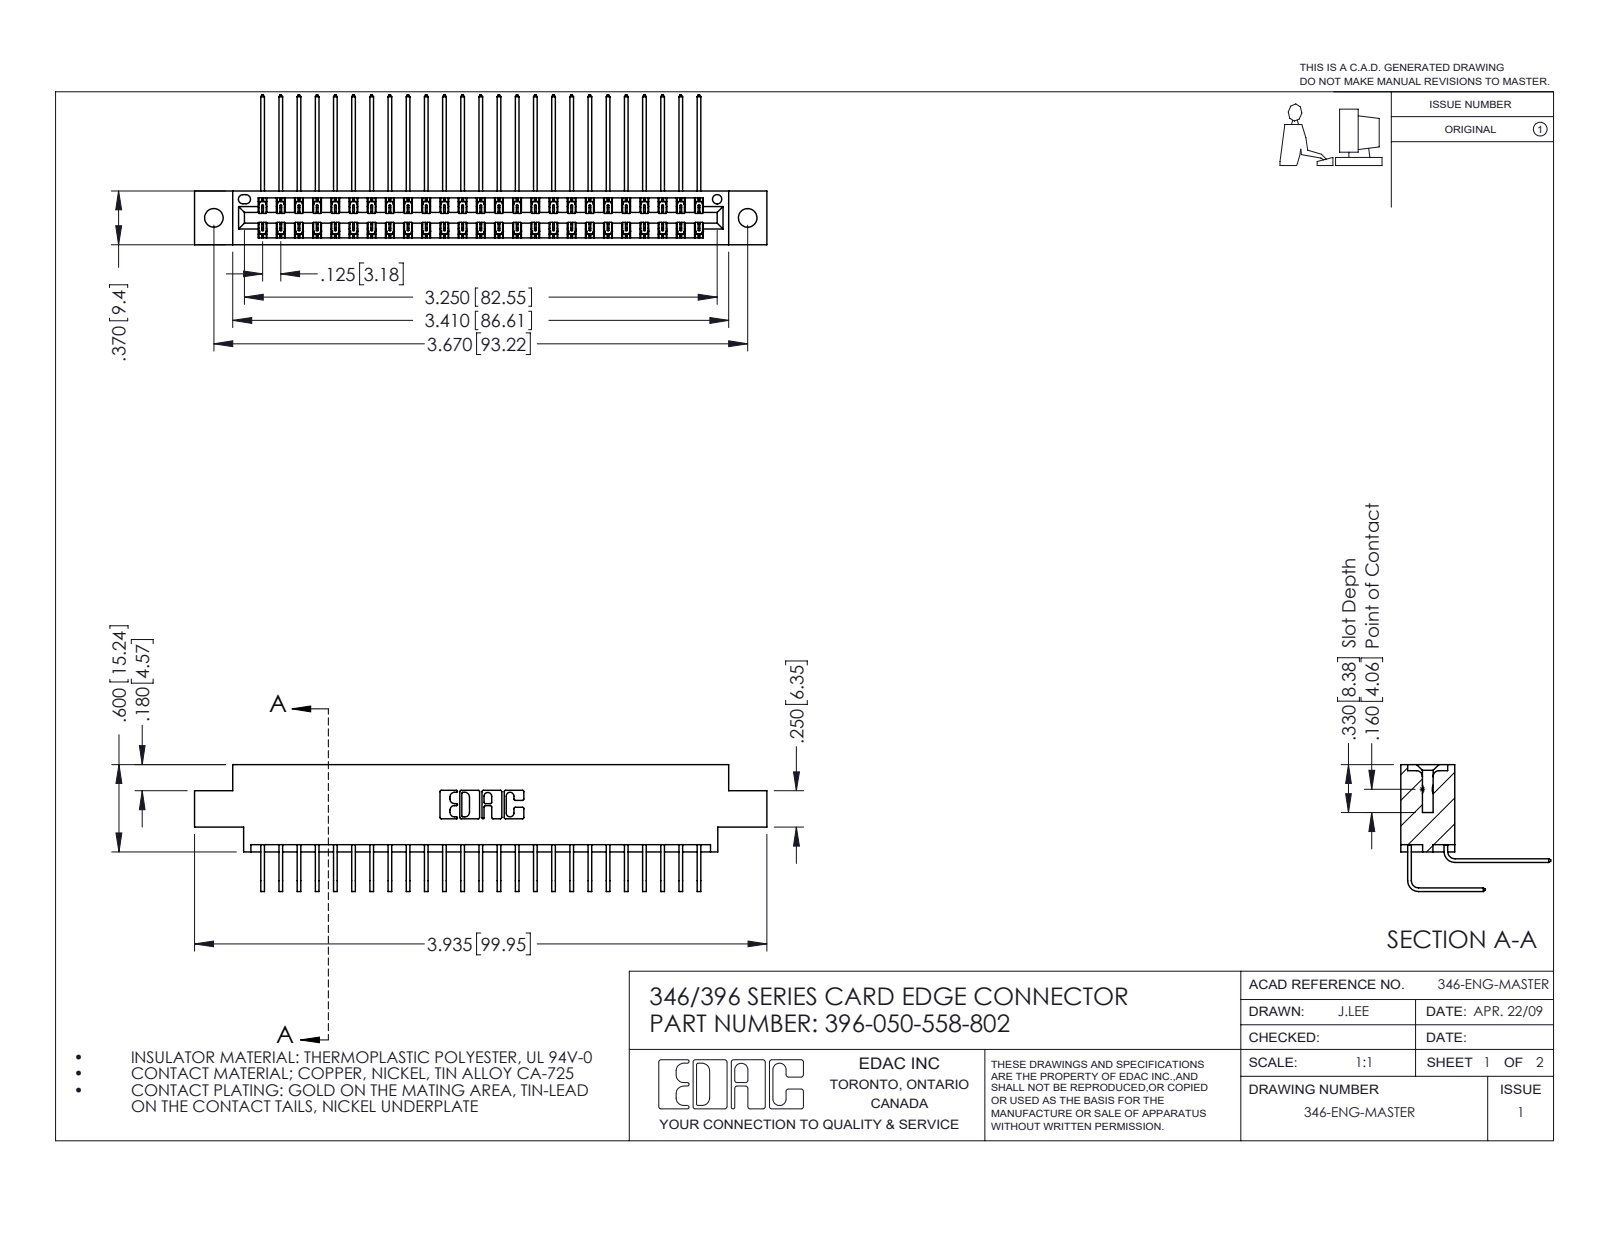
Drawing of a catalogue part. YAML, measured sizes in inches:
part_name: "346 Part_0.170 Offset - 0.128 Dia; 345-292-001_558 Tail - 2; 345-292-001_558 559 Tail - 1; 396-050-558-802"
step_written_by: "SolidWorks 2016 (CONFIG_CONTROL_DESIGN)"
units: inches
bodies: {solids: 51, faces: 2826, planar: 1930, cylindrical: 896, other: 0}
overall_size: [3.935, 1.03, 0.873]
volume: 0.593
surface_area: 22.28
round_holes:
  - {diameter: 0.128, count: 2}
  - {diameter: 0.064, count: 1}
partial_cylinders:
  - {radius: 0.006, count: 75}
  - {radius: 0.01, count: 22}
  - {radius: 0.007, count: 6}
  - {radius: 0.031, count: 6}
  - {radius: 0.026, count: 3}
  - {radius: 0.014, count: 2}
  - {radius: 0.022, count: 2}
  - {radius: 0.024, count: 2}
face_to_face_distances: [0.322, 0.048, 0.025, 0.37, 0.25, 0.298, 0.072, 0.275, 0.148, 0.222]
hole_center_spacings: [0.246, 3.462, 3.67]
